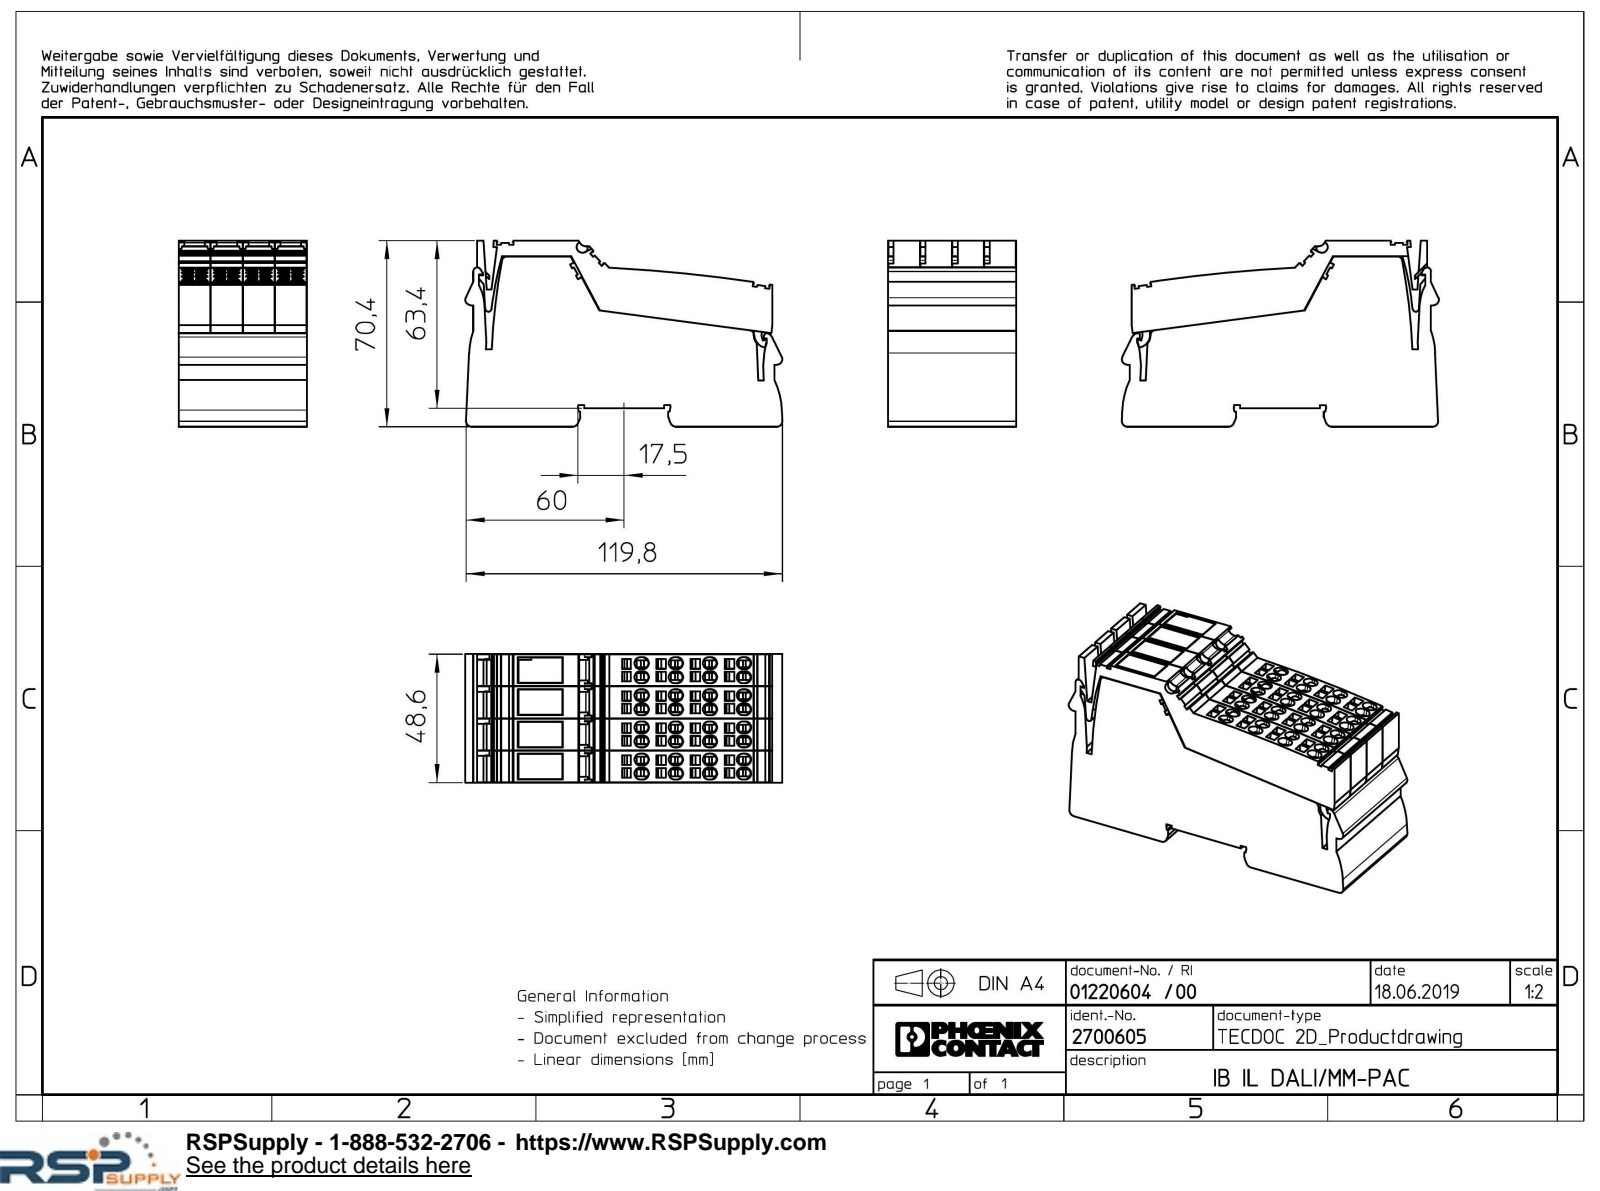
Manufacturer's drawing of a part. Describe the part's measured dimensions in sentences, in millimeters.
The part is named "L_L_8_GEH_GN_6021-select; L-L_ST_GN_6021-select; L_L_LWL_OG_HKS_7K-select.2; L_L_LWL_OG_HKS_7K_AUSSEN-select (+2 more)". Its 3-D file was written by "Creo Elements/Direct Modeling 20.1A 29-Sep-2018 (C) Parametric Technology GmbH (AUTOMOTIVE_DESIGN)". It is 9 solids with 2113 faces: 1820 planar, 181 cylindrical and 112 other. Overall it measures 120.11 by 70.43 by 48.6 millimeters. Its volume is 318 858 cubic millimeters and its surface area 84 249 square millimeters. Round holes: 24 of diameter 1.2. Partial cylindrical surfaces (rounded edges, fillets, slot ends): 64 of radius 2.25, 8 of radius 0.6, 6 of radius 2, 2 of radius 0.15, 2 of radius 1.7, 2 of radius 8.5, 2 of radius 9.5, 2 of radius 16.7. The main face-to-face distances are 12.15, 24.3, 12, 48.6, 24.15, 36.45, 12.3, 36.3, 25.99, 13. The hole center spacings are 17.8, 12.15, 13, 13.86, 27.56, 4.8, 14.94, 21.36.
